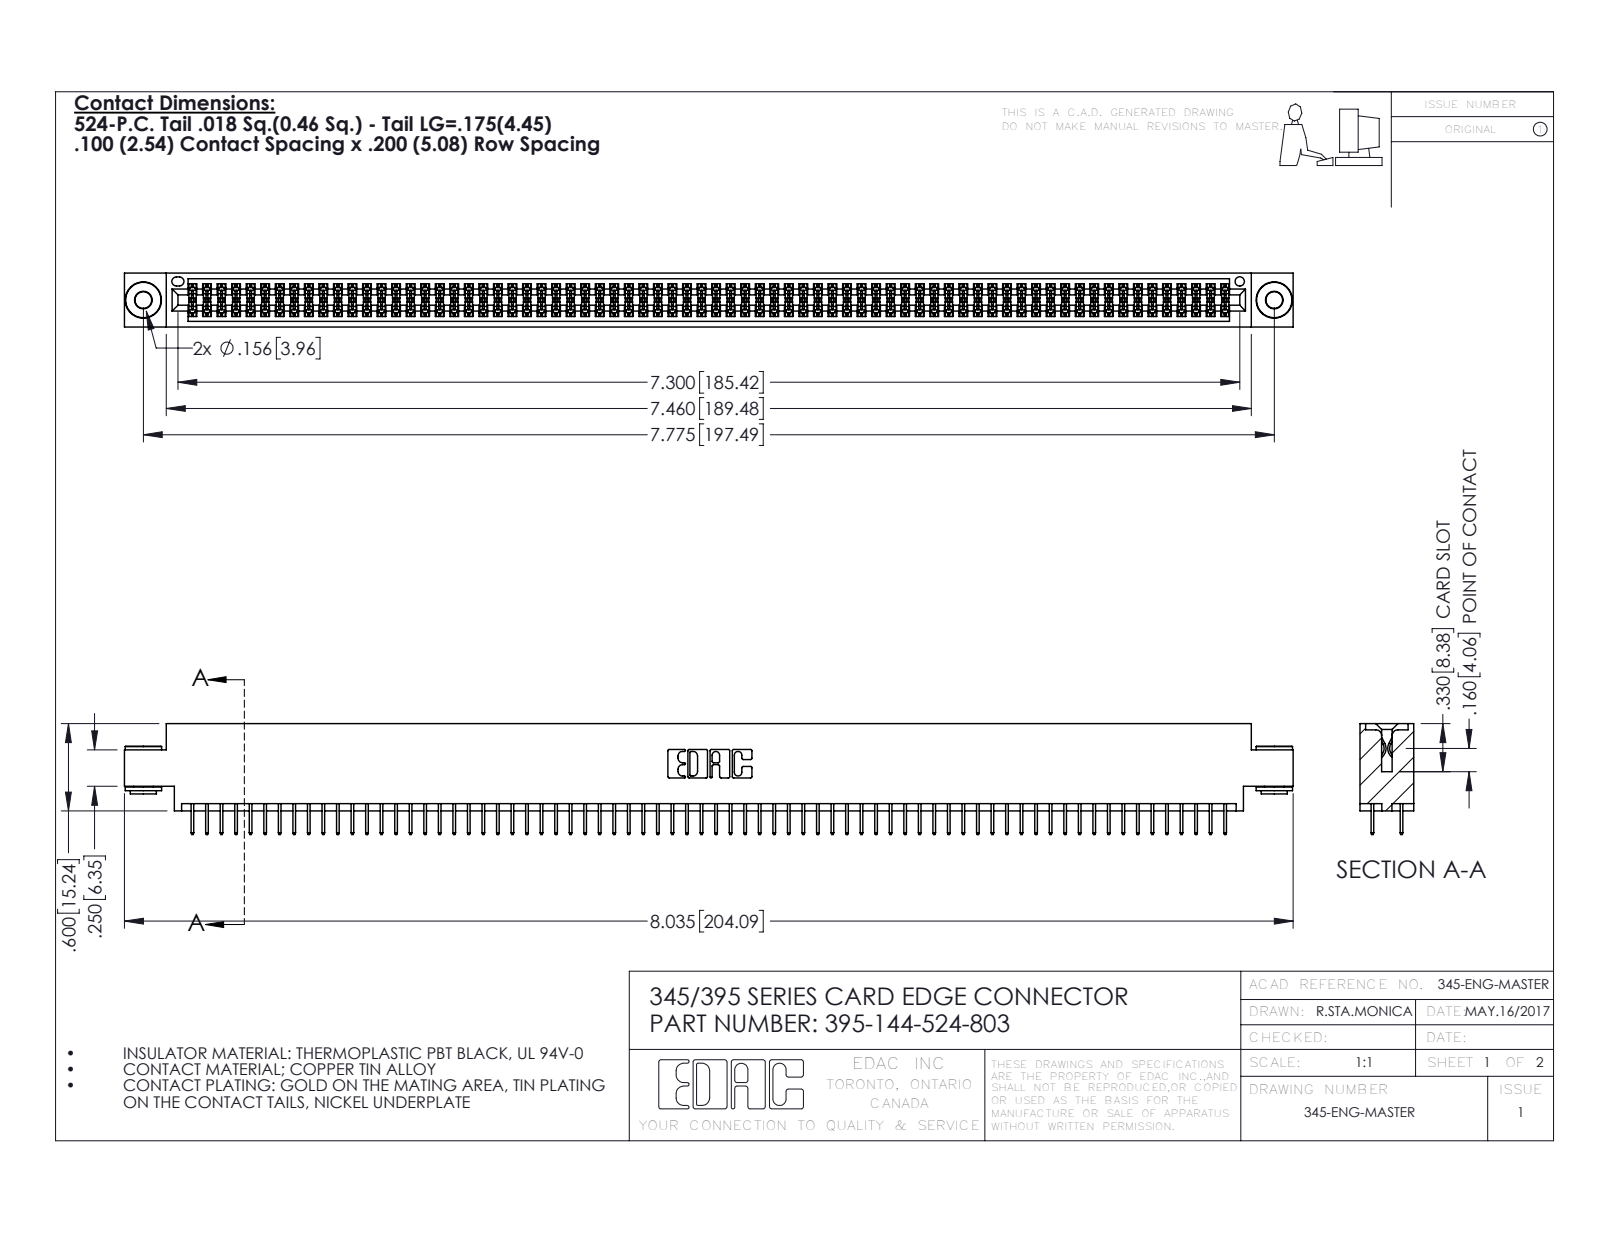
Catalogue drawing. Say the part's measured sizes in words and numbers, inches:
The part is named "345-250-002_345-250-002-102; 345 Part_0.170 Offset - 0.156 Dia-TH; 345-292-001_345-293-124; 395-144-524-803". Its 3-D file was written by "SolidWorks 2016 (CONFIG_CONTROL_DESIGN)". It is 147 solids with 7944 faces: 5710 planar, 2226 cylindrical and 8 other. Overall it measures 8.035 by 0.762 by 0.37 inches. Its volume is 1.208 cubic inches and its surface area 45.9 square inches. Round holes: 2 of diameter 0.116, 2 of diameter 0.156, 1 of diameter 0.064. Round bosses or shafts: 2 of diameter 0.25, 2 of diameter 0.18, 2 of diameter 0.136. Partial cylindrical surfaces (rounded edges, fillets, slot ends): 216 of radius 0.006, 22 of radius 0.01, 6 of radius 0.007, 6 of radius 0.031, 3 of radius 0.026, 2 of radius 0.014, 2 of radius 0.019, 2 of radius 0.022. The main face-to-face distances are 0.072, 0.298, 0.37, 0.2, 0.098, 0.272, 0.025, 0.225, 0.072, 0.175. The hole center spacings are 0.27, 7.539, 7.775.
